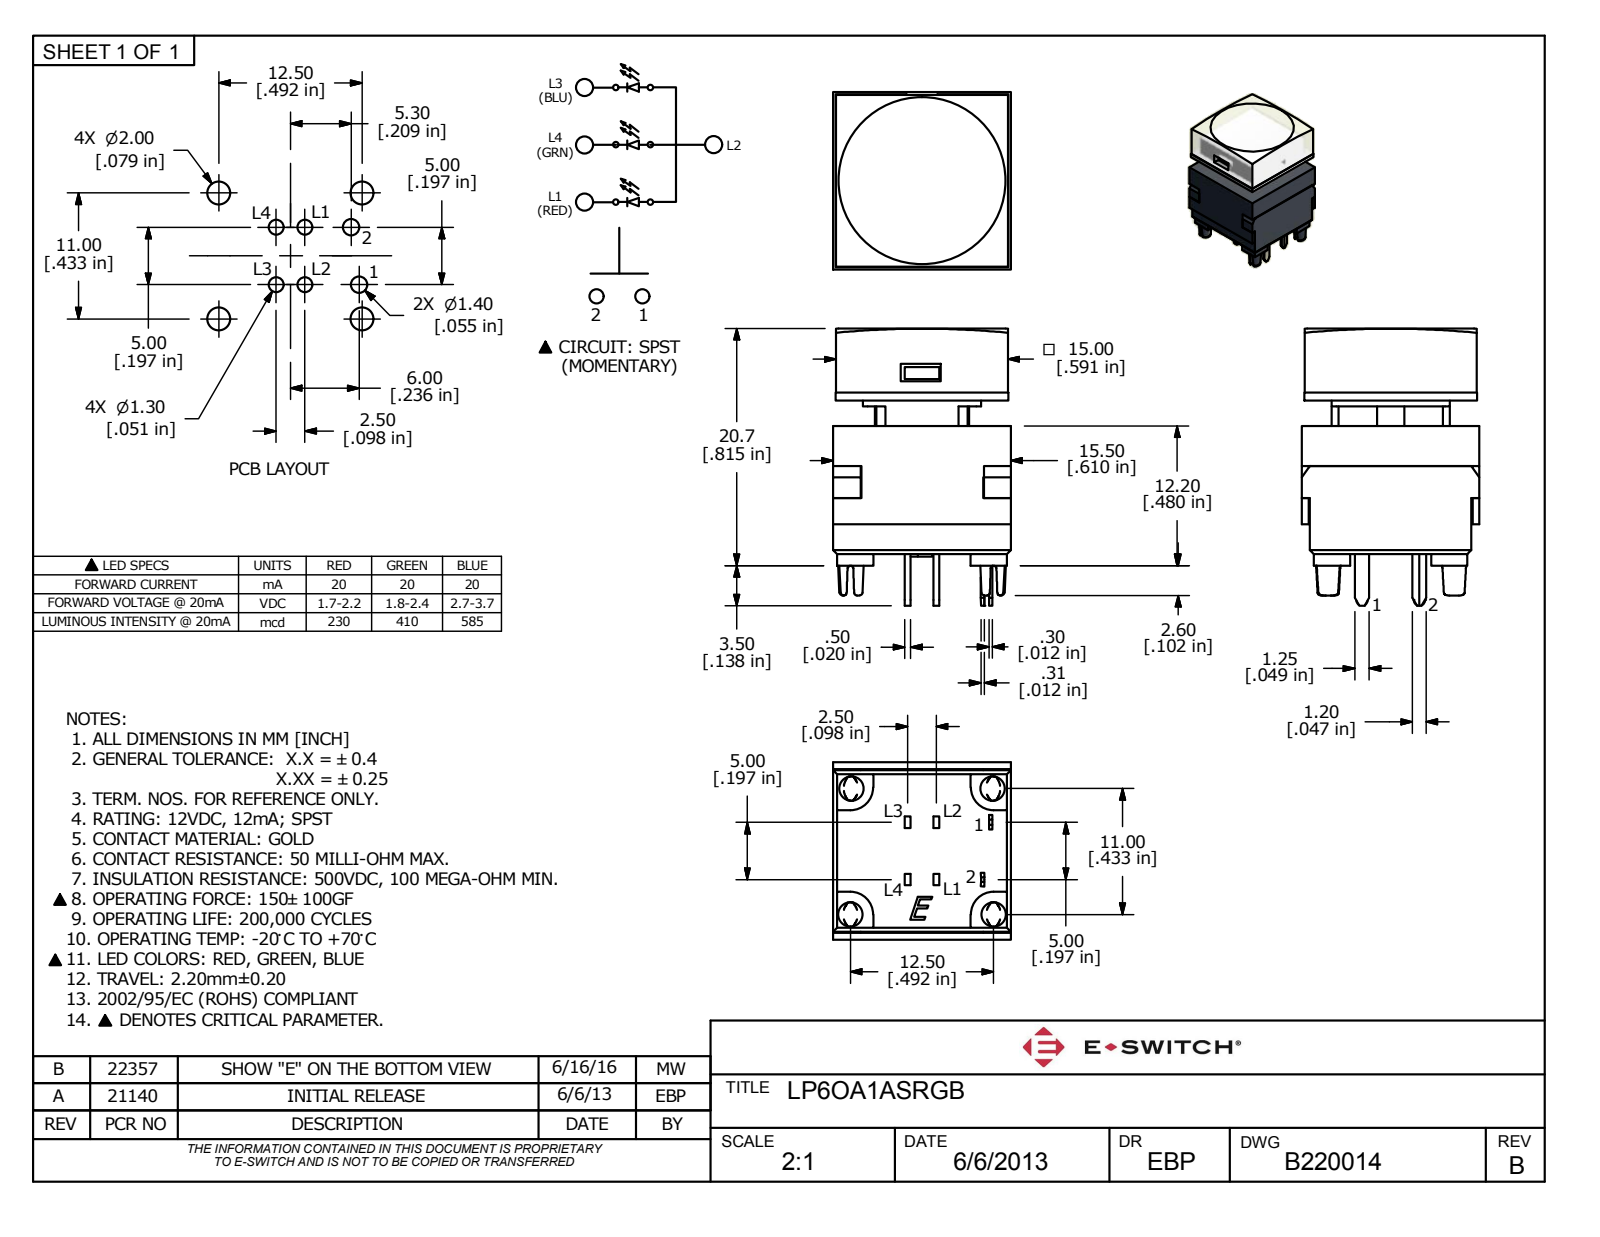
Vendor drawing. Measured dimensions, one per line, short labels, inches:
name: P:\\E-Switch Secure\\3D_MODELS_STP_FORMAT\\LP6OA1ASRGB.stp
written by: ACIS (CONFIG_CONTROL_DESIGN)
unit: in
bodies: 1 solid, 377 faces (296 planar, 61 cylindrical, 20 other)
size: 0.953 × 0.61 × 0.61
volume: 0.15 in³; area: 7.948 in²
bosses: 2× ⌀0.031
rounds: 16× R0.016, 12× R0.008, 6× R0.01, 4× R0.012, 4× R0.079, 2× R0.02, 2× R0.024, 2× R0.198
face distances: 0.024, 0.047, 0.028, 0.563, 0.528, 0.6, 0.553, 0.551, 0.049, 0.61
